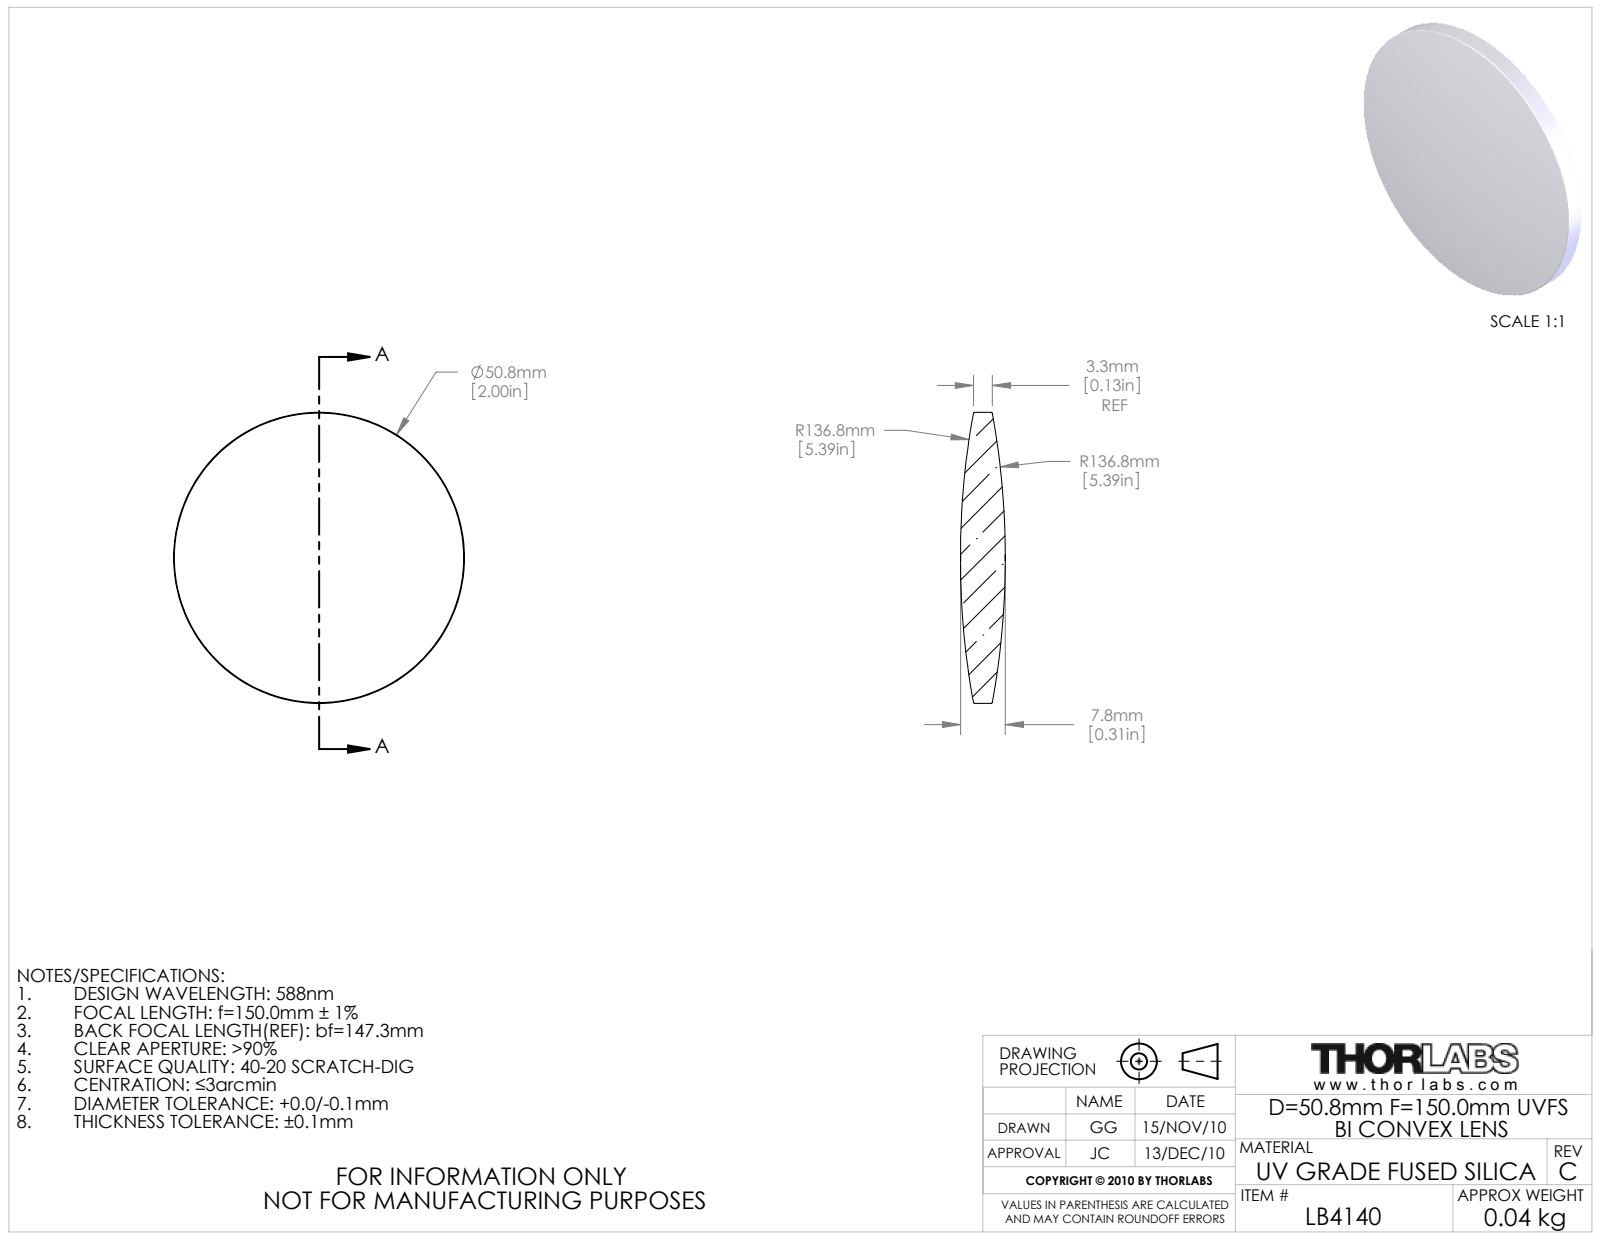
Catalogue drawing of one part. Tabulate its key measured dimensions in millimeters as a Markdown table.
| quantity | value |
| --- | --- |
| part name | 3416-E0W |
| STEP written by | SolidWorks 2009 (AUTOMOTIVE_DESIGN) |
| units | millimeters |
| bodies | 1 solid, 10 faces (0 planar, 2 cylindrical, 8 other) |
| overall size | 50.8 × 50.8 × 7.8 |
| volume | 11 252 mm³ |
| surface area | 4 584 mm² |
| round bosses / shafts (diameter × count) | 50.8 × 1 |
